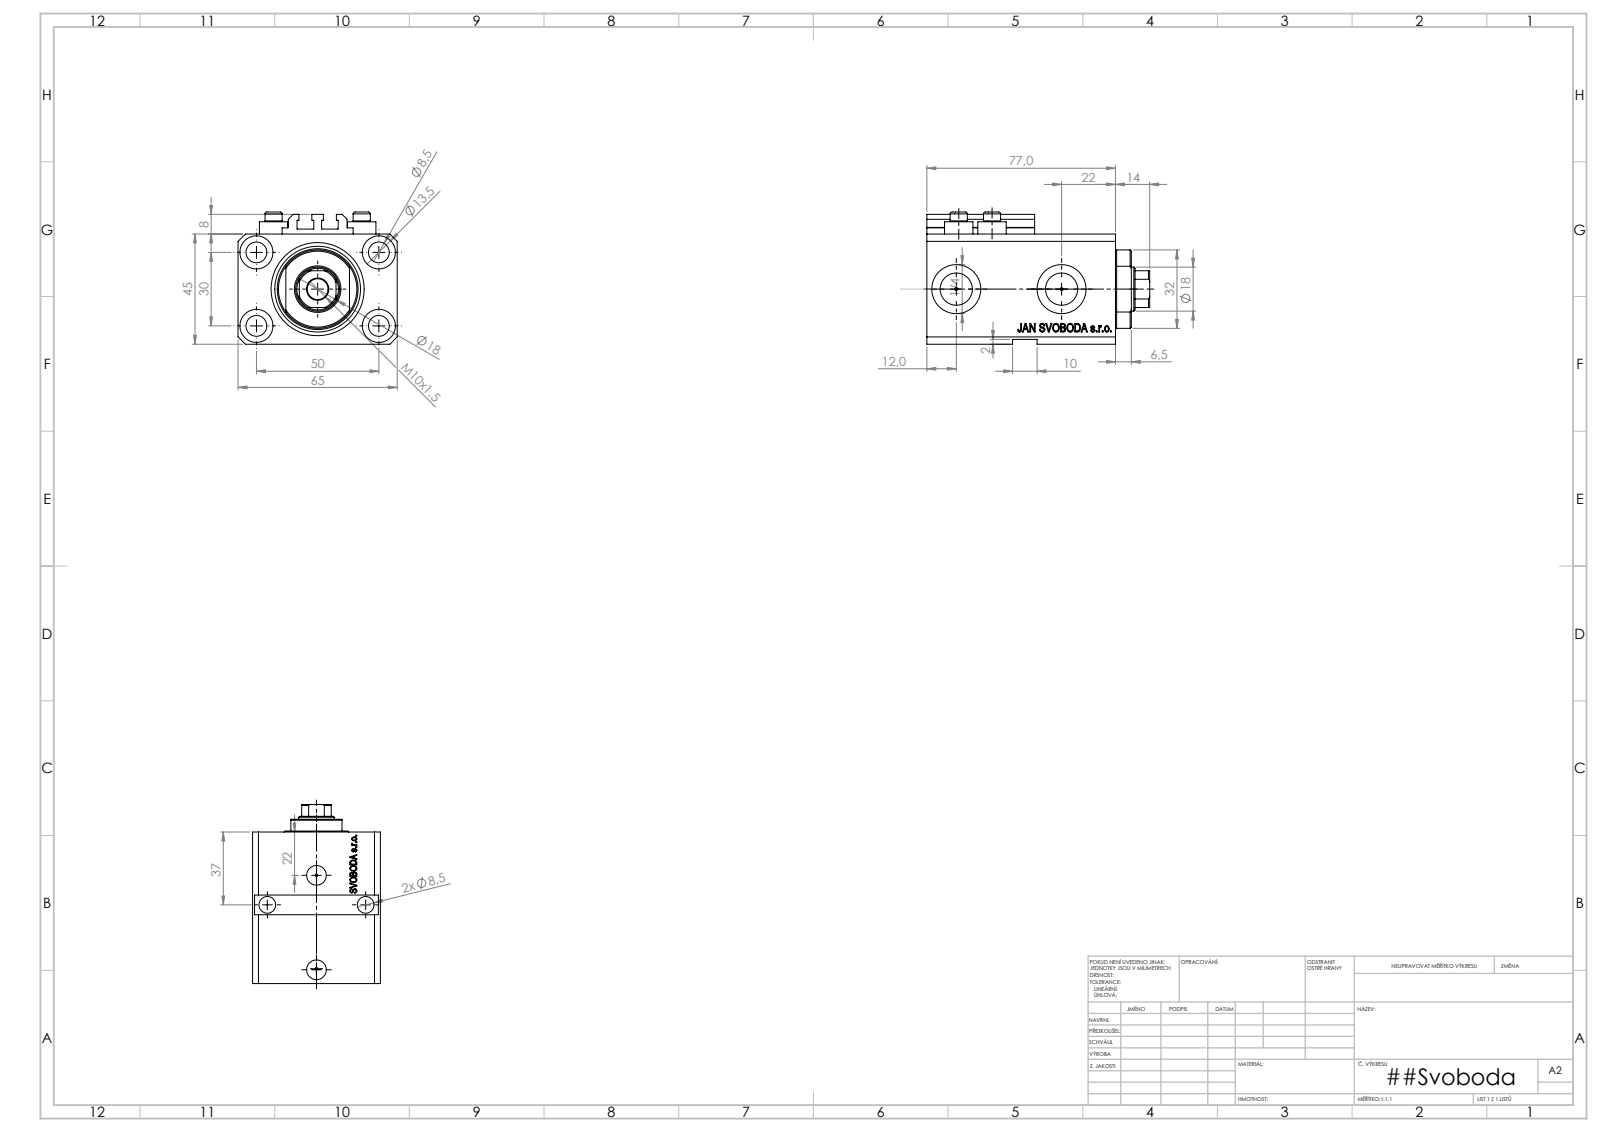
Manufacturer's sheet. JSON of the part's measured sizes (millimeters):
{"part_name": "V250CE_VC_E; V250CE_E_Body; V250CE_C_VCP; ALLEN BOLT V250CE", "step_written_by": "SolidWorks 2019 (CONFIG_CONTROL_DESIGN)", "units": "millimeters", "bodies": {"solids": 8, "faces": 1067, "planar": 511, "cylindrical": 126, "other": 430}, "overall_size": [91, 65, 54], "volume_mm3": 199775, "surface_area_mm2": 59185, "round_holes": [[8.5, 7], [1.25, 4], [4, 4], [13.5, 4], [10, 2], [13.16, 2], [20, 2], [18, 1], [25, 1], [38, 1]], "round_bosses_or_shafts": [[11.6, 4], [7, 4]], "partial_cylinders_radius": [[0.2, 10], [8.5, 1], [16, 1]], "face_to_face_distances": [45, 65, 63, 14, 77, 2, 6.9, 56.1, 70.1, 47], "hole_center_spacings": [29.15, 50, 13.6, 15.12, 18.81, 18.97, 26.22, 26.61]}
